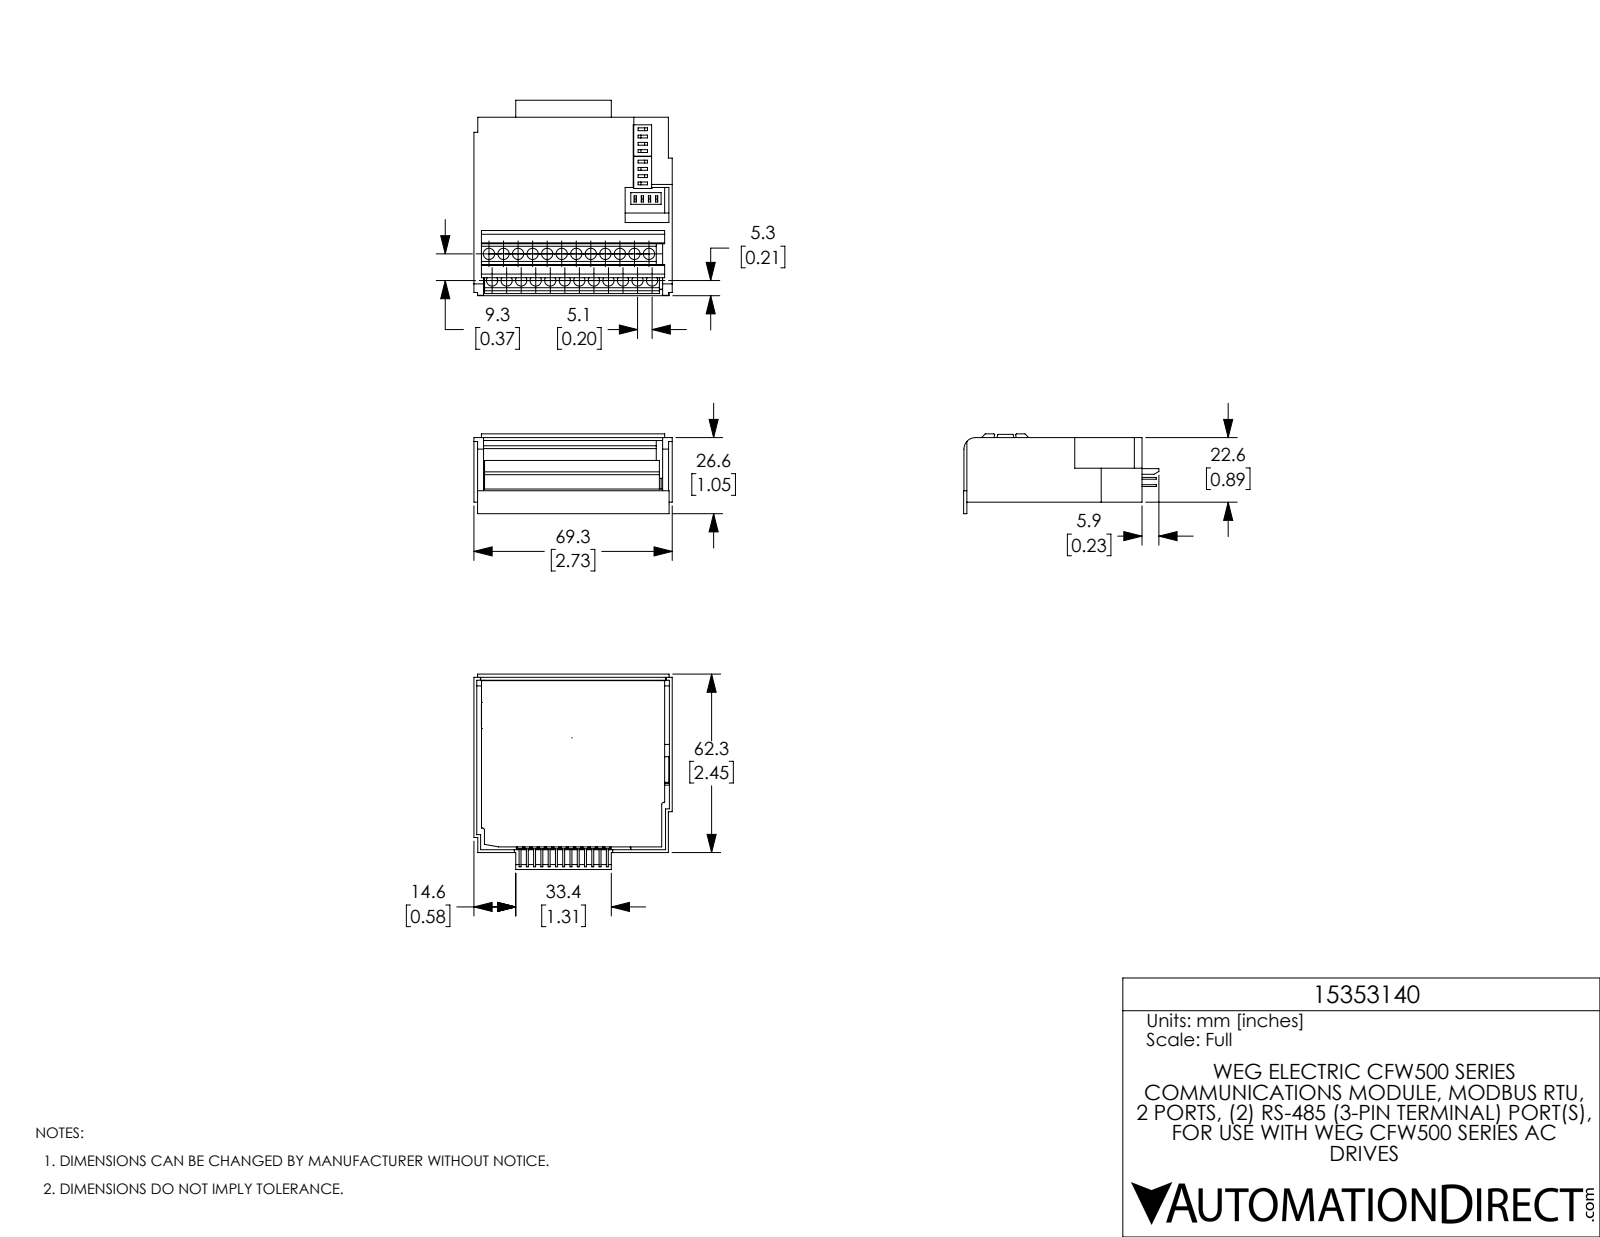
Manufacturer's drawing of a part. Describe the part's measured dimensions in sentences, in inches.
The part is named "15353140_MODULO COMUNICACAO CFW500_CRS485_B Coord nc". Its 3-D file was written by "SolidWorks 2017 (AUTOMOTIVE_DESIGN)". It is 2 solids with 553 faces: 499 planar, 54 cylindrical and 0 other. Overall it measures 2.726 by 2.685 by 1.096 inches. Its volume is 1.844 cubic inches and its surface area 47.09 square inches. Round holes: 12 of diameter 0.154, 12 of diameter 0.155. Partial cylindrical surfaces (rounded edges, fillets, slot ends): 2 of radius 0.03, 1 of radius 0.118, 1 of radius 0.157. The main face-to-face distances are 0.039, 0.063, 0.73, 0.667, 0.707, 0.77, 2.687, 2.727, 0.051, 1.704. The hole center spacings are 0.2, 0.4, 0.6, 0.8, 1, 0.369, 1.2, 0.399.
